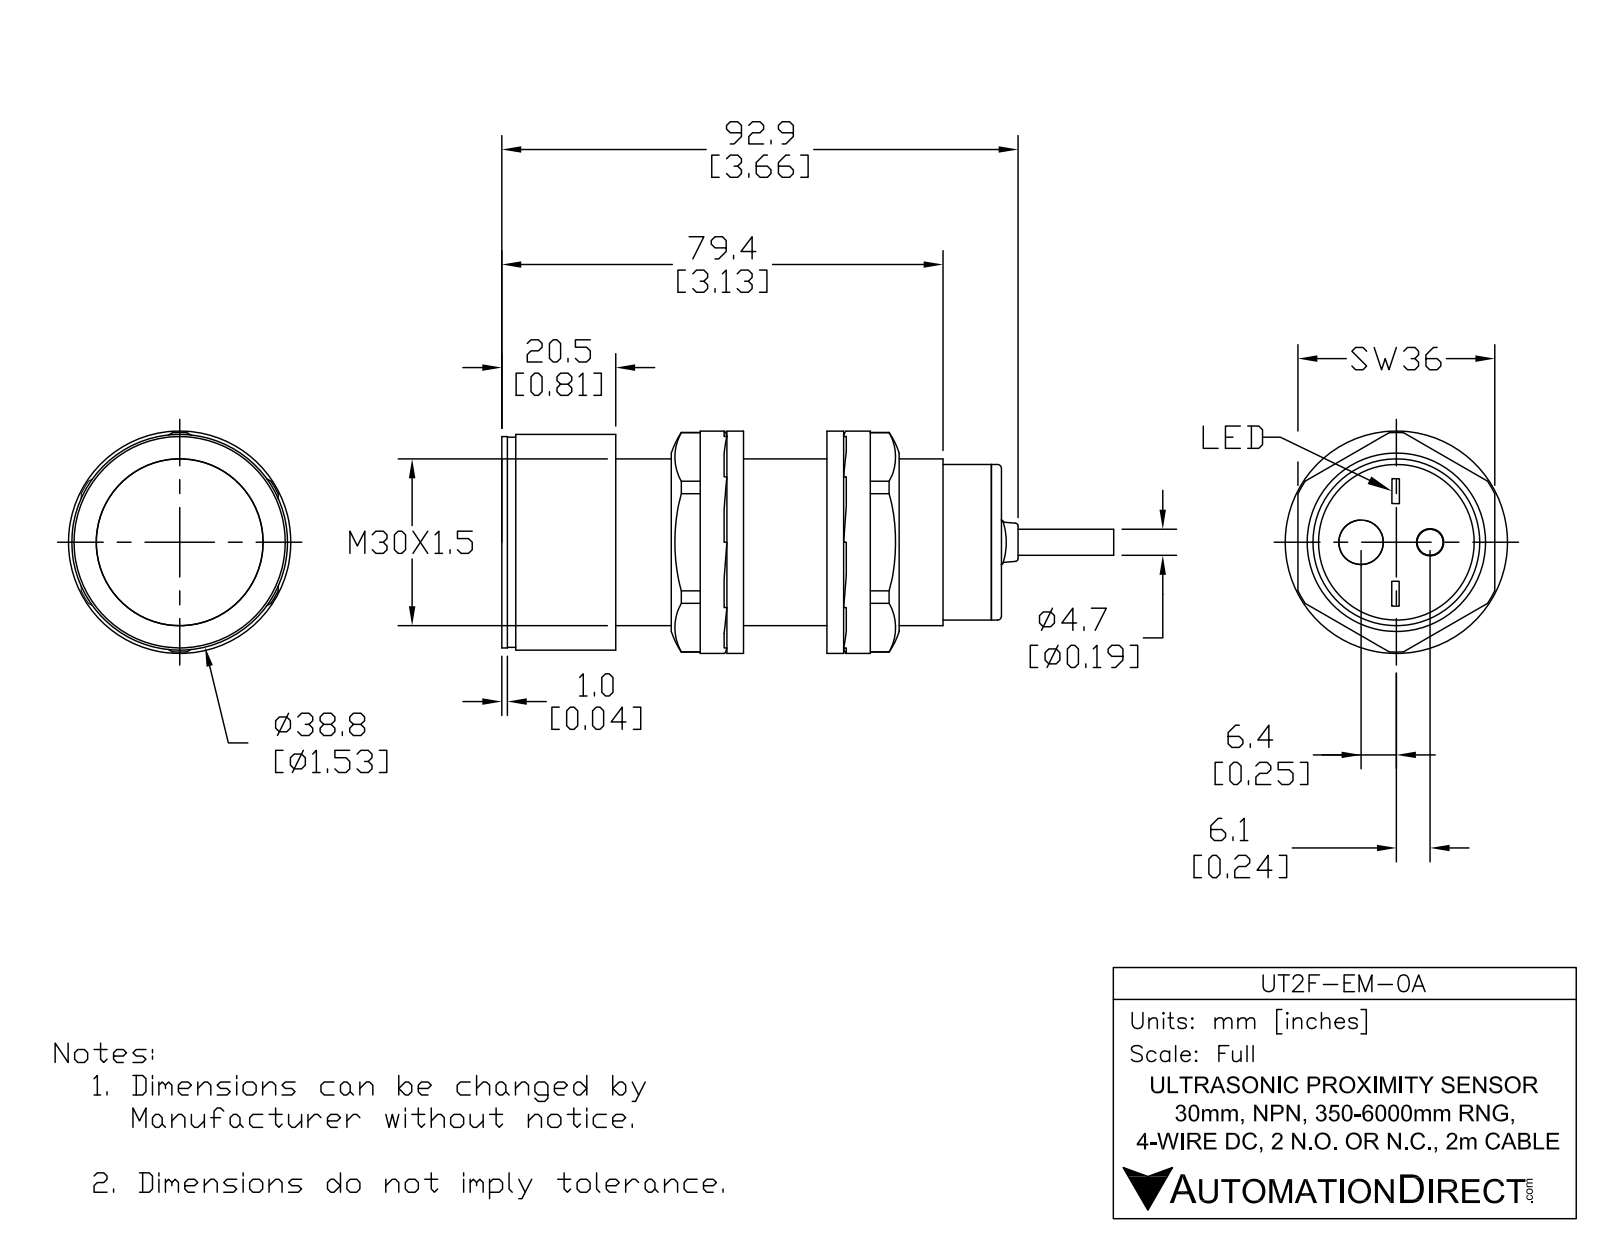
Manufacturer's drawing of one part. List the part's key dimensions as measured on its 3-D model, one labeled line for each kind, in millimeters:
Part name (STEP PRODUCT): UT2F-EM-0A
STEP written by: SolidWorks 2017 (AUTOMOTIVE_DESIGN)
Units: millimetres
Bodies: 5 solids, 49 faces (14 planar, 20 cylindrical, 15 other)
Overall size (bounding box): 128.1 × 38.8 × 38.8
Volume: 71 780 mm³ · Surface area: 15 500 mm²
Round holes (diameter × count): ⌀4.7 ×1, ⌀8 ×1, ⌀33 ×1
Round bosses / shafts (diameter × count): ⌀38.8 ×1, ⌀37.8 ×1, ⌀30 ×1, ⌀28 ×1
Main face-to-face distances: 85.6, 1.5, 87.1, 19.5, 18, 67.6, 88.9, 87.4, 69.4, 1.8
Hole centre spacings: 6.1, 6.4, 12.4
